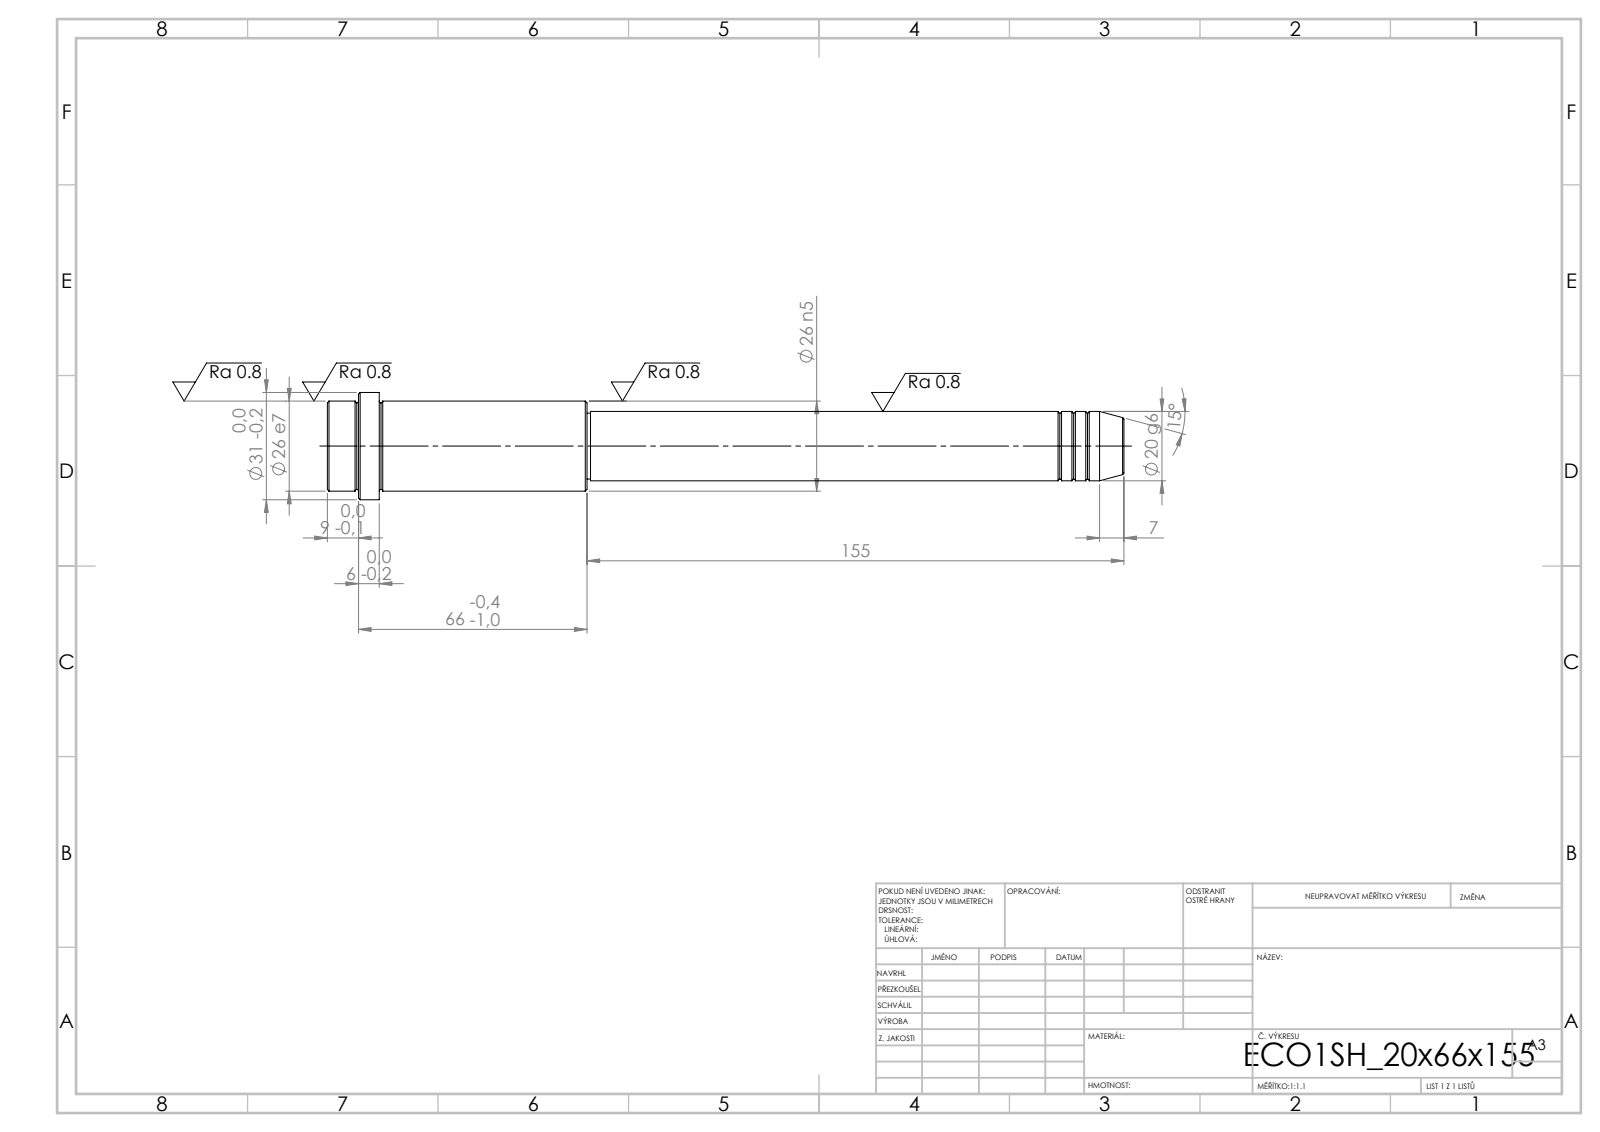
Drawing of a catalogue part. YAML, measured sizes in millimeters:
step_written_by: "SolidWorks 2019 (CONFIG_CONTROL_DESIGN)"
units: millimeters
bodies: {solids: 1, faces: 52, planar: 6, cylindrical: 16, other: 30}
overall_size: [230, 31, 31]
volume: 89271
surface_area: 17495
round_bosses_or_shafts:
  - {diameter: 31, count: 1}
  - {diameter: 26, count: 1}
  - {diameter: 20, count: 1}
  - {diameter: 19, count: 1}
face_to_face_distances: [15, 60, 75, 155, 215, 230, 221, 66, 6, 9]
